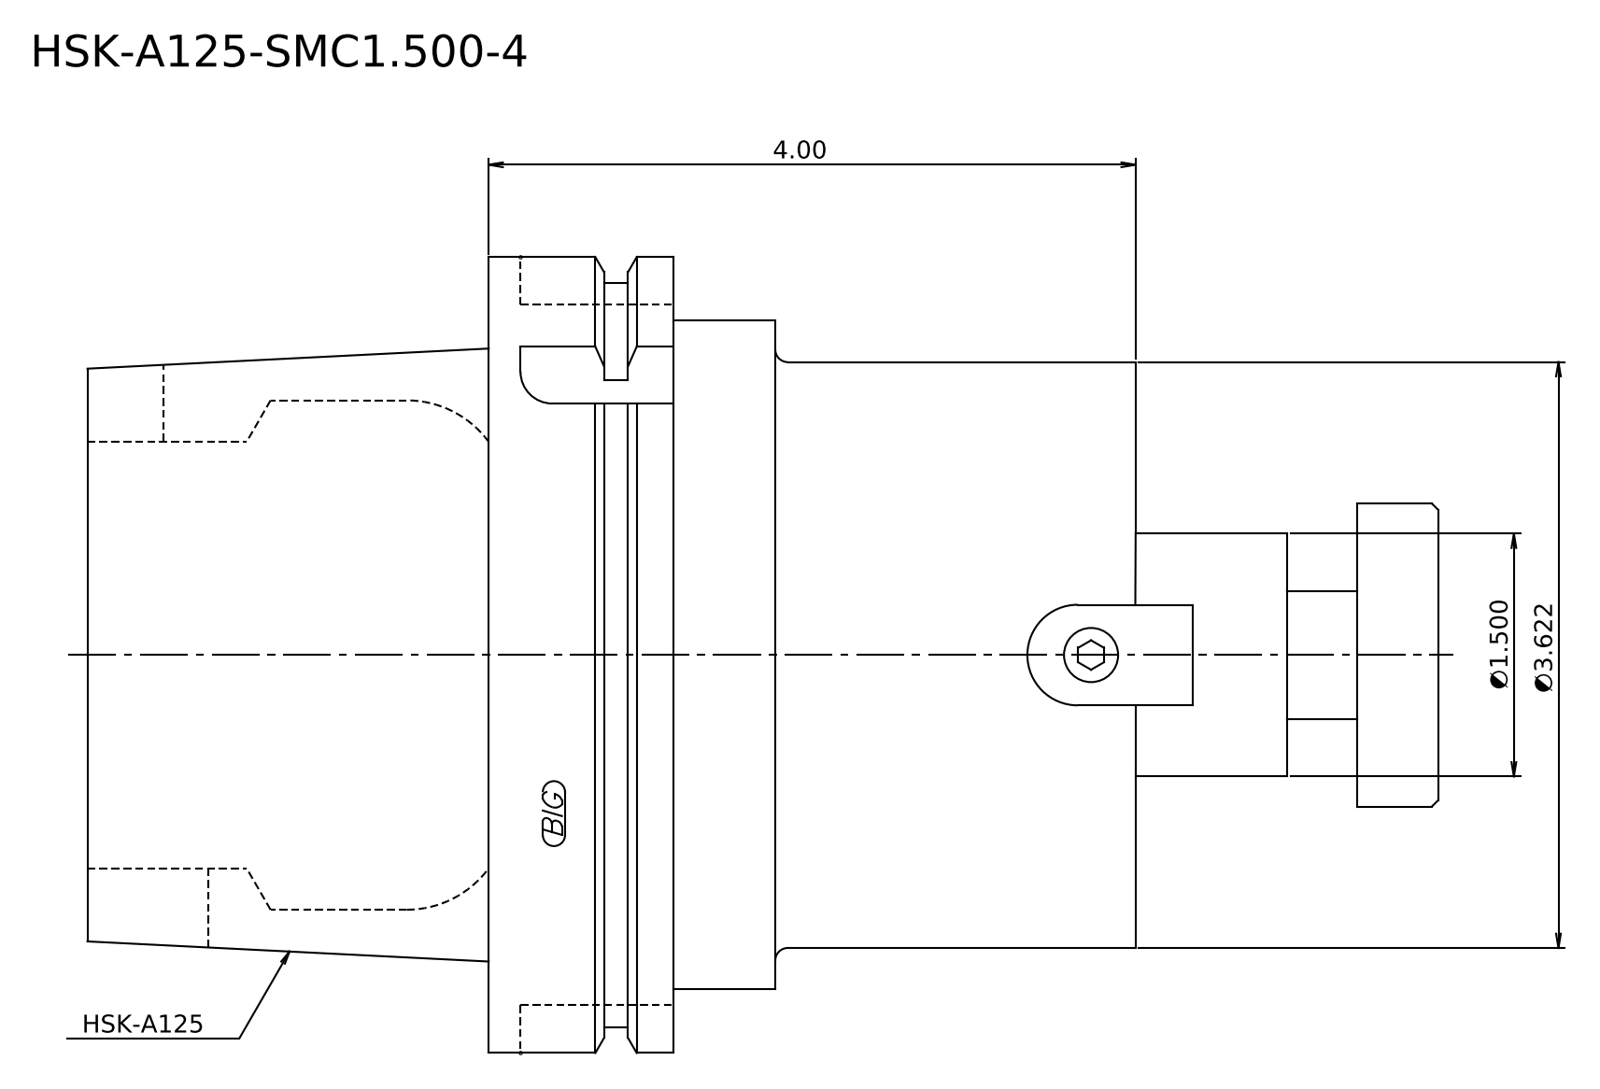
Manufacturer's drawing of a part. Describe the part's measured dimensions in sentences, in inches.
Its 3-D file was written by "Kubotek KeyCreator 2011 V10.0.2 (22737) (automotive_design)". It is 1 solid with 18 faces: 8 planar, 6 cylindrical and 4 other. Overall it measures 7.417 by 4.921 by 4.921 inches. Its volume is 80.61 cubic inches and its surface area 123.6 square inches. Round bosses or shafts: 1 of diameter 4.921, 1 of diameter 4.606, 1 of diameter 4.134, 1 of diameter 3.622, 1 of diameter 1.5. The main face-to-face distances are 6.48, 4, 2.48, 2.858, 1.142, 3.622, 2.228, 0.63, 1.772, 4.252.
